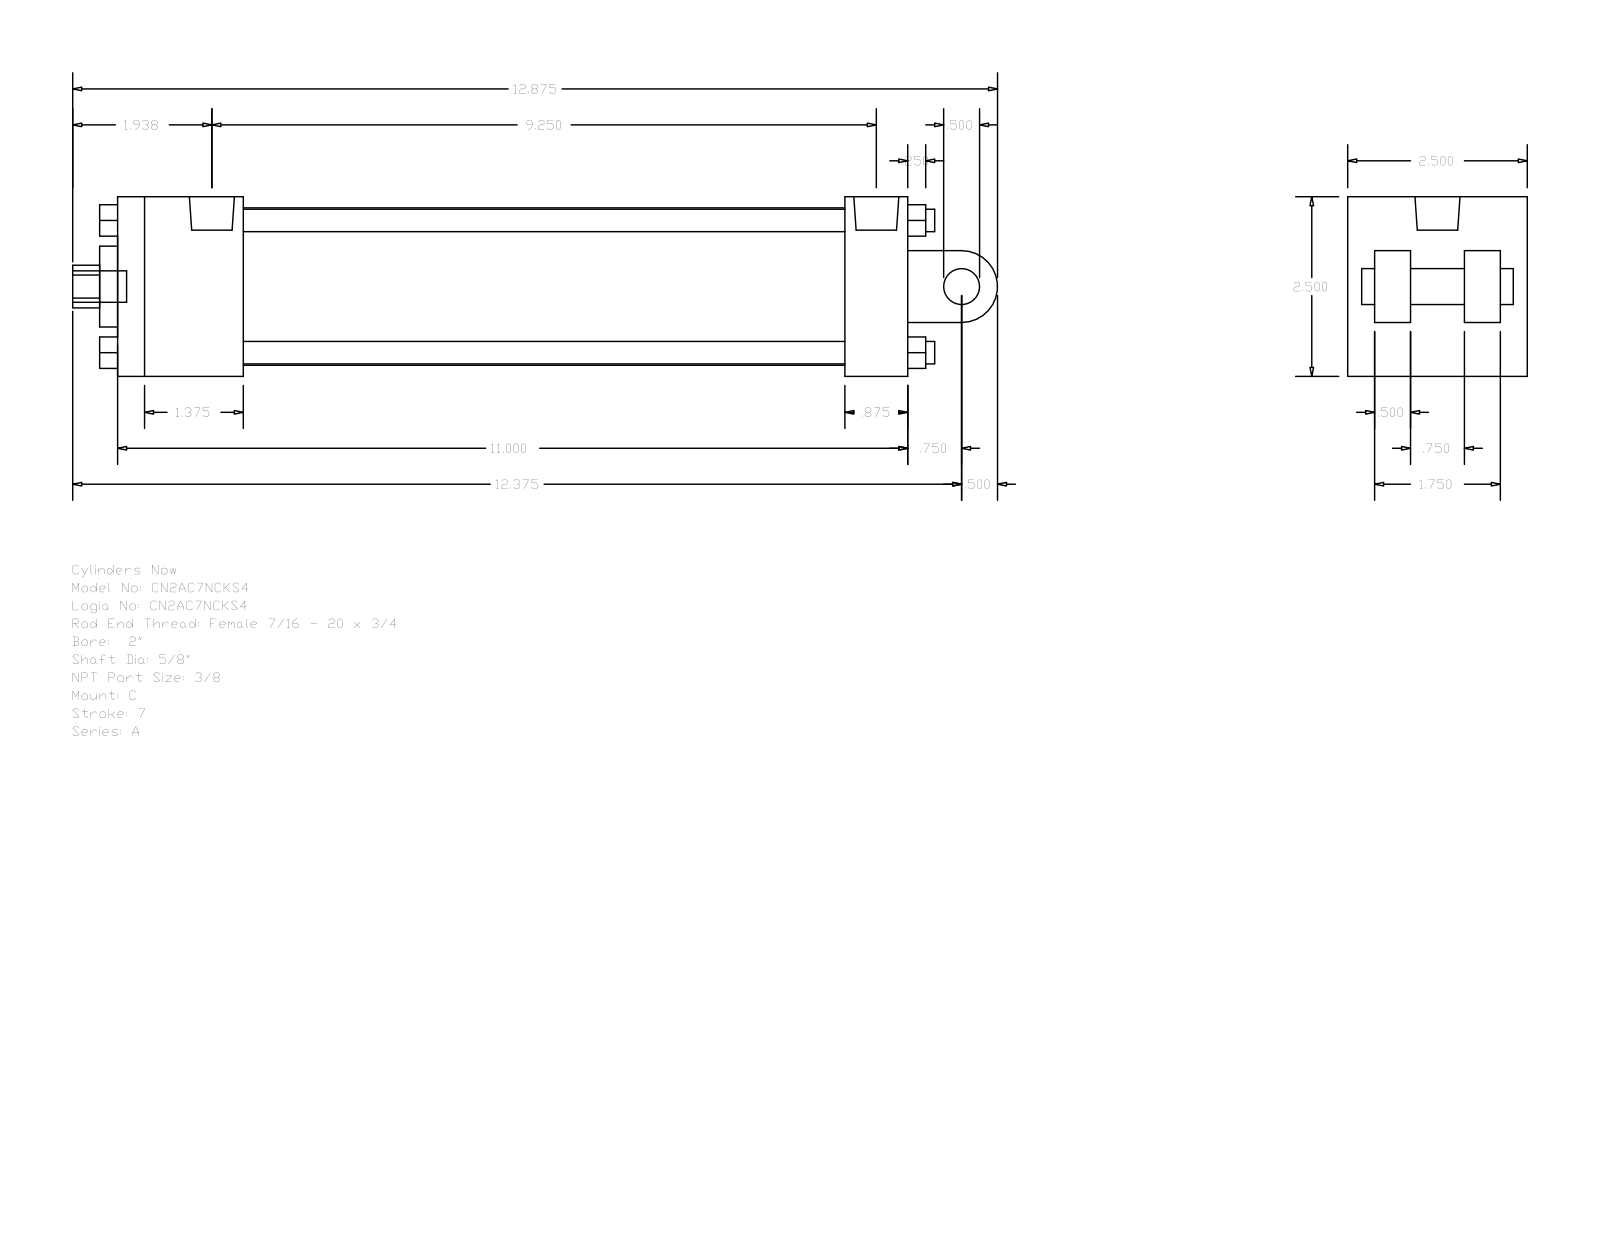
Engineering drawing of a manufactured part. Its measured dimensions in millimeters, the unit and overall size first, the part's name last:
Units: millimetres
Overall size (bounding box): 327.02 × 63.5 × 63.5
Round holes (diameter × count): ⌀5.56 ×2, ⌀15.88 ×1, ⌀15.93 ×1, ⌀28.57 ×1, ⌀55.63 ×1
Round bosses / shafts (diameter × count): ⌀7.94 ×4, ⌀5.56 ×2, ⌀15.93 ×1, ⌀12.7 ×1, ⌀11.11 ×1
Partial cylindrical surfaces — rounded edges, fillets, slot ends (radius × count): R7.54 ×1, R12.7 ×1
Main face-to-face distances: 63.5, 279.39, 22.22, 44.45, 234.94, 257.17, 212.72, 12.7, 41.28, 9.52
Hole centre spacings: 3.97
Bodies: 0 solids, 135 faces (102 planar, 33 cylindrical, 0 other)
Part name (STEP PRODUCT): A_C__0200_0.625
STEP written by: GSSL Pune (CONFIG_CONTROL_DESIGN)
